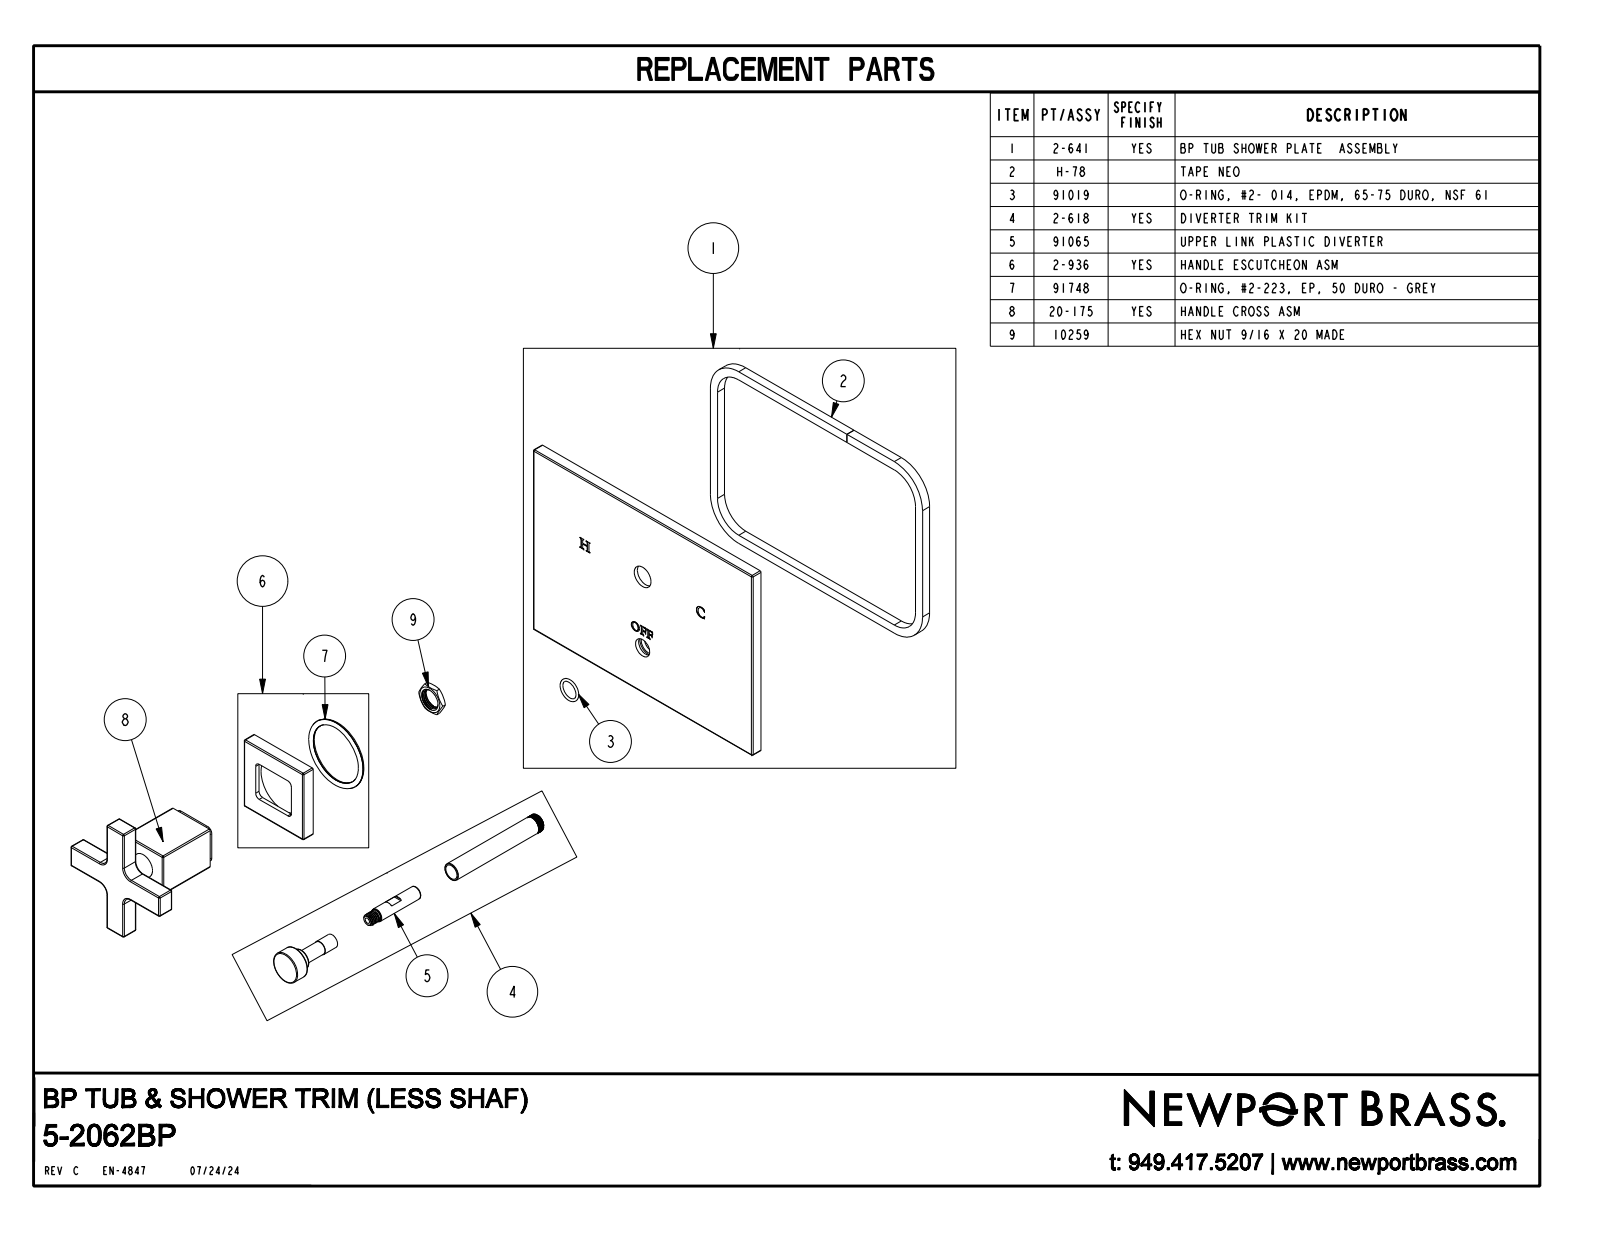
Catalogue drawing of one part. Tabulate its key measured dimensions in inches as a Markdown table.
| quantity | value |
| --- | --- |
| part name | 5-2062BP |
| STEP written by | CREO PARAMETRIC BY PTC INC, 2018400 (CONFIG_CONTROL_DESIGN) |
| units | inches |
| bodies | 1 solid, 368 faces (74 planar, 70 cylindrical, 224 other) |
| overall size | 7.75 × 5.5 × 3.356 |
| volume | 19.34 in³ |
| surface area | 119.7 in² |
| round bosses / shafts (diameter × count) | 0.84 × 1, 0.65 × 1, 0.54 × 1, 0.523 × 1, 0.354 × 1 |
| partial cylindrical surfaces (radius × count) | 0.03 × 48, 0.25 × 4 |
| main face-to-face distances | 0.31, 3.356, 3.046, 3.205, 4.545, 2.906, 2.596, 0.45, 0.66, 0.35 |
